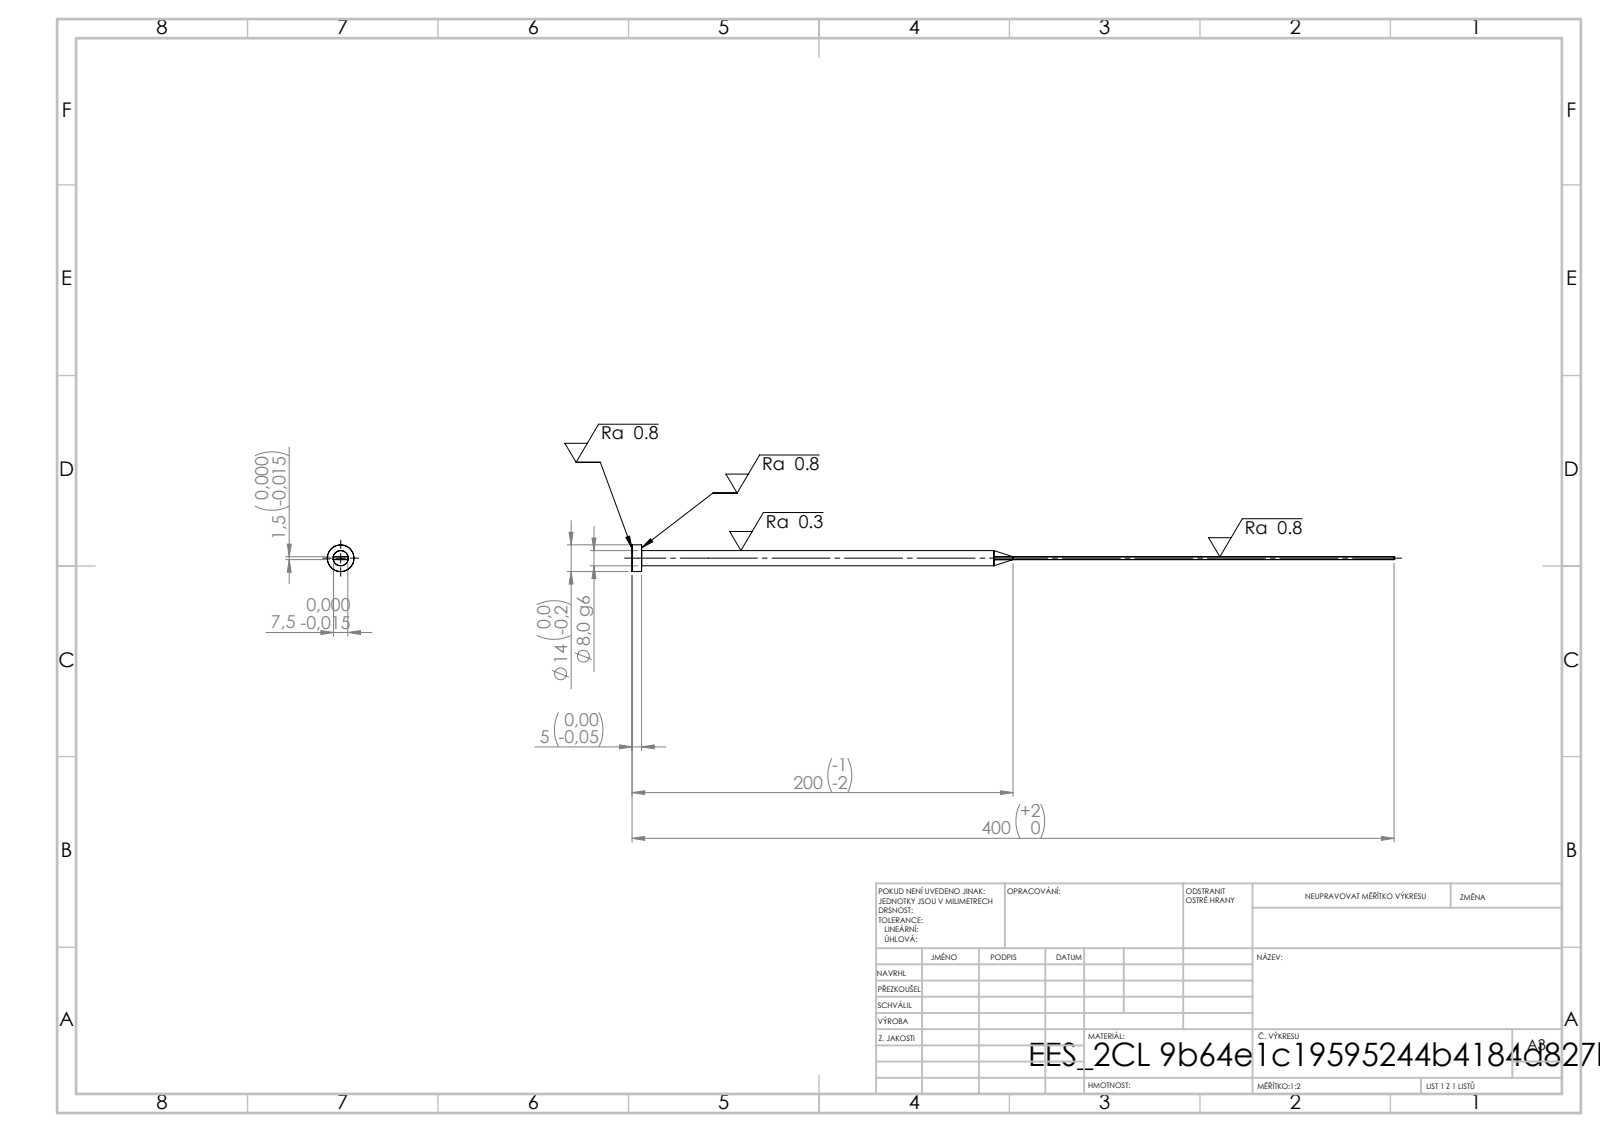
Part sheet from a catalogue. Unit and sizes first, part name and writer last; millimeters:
Units: millimetres
Overall size (bounding box): 400 × 14 × 14
Round bosses / shafts (diameter × count): ⌀14 ×1, ⌀8 ×1
Main face-to-face distances: 1.5, 7.5, 5, 400, 395
Volume: 12 611 mm³ · Surface area: 8 949 mm²
Bodies: 1 solid, 15 faces (7 planar, 4 cylindrical, 4 other)
STEP written by: SolidWorks 2019 (CONFIG_CONTROL_DESIGN)
